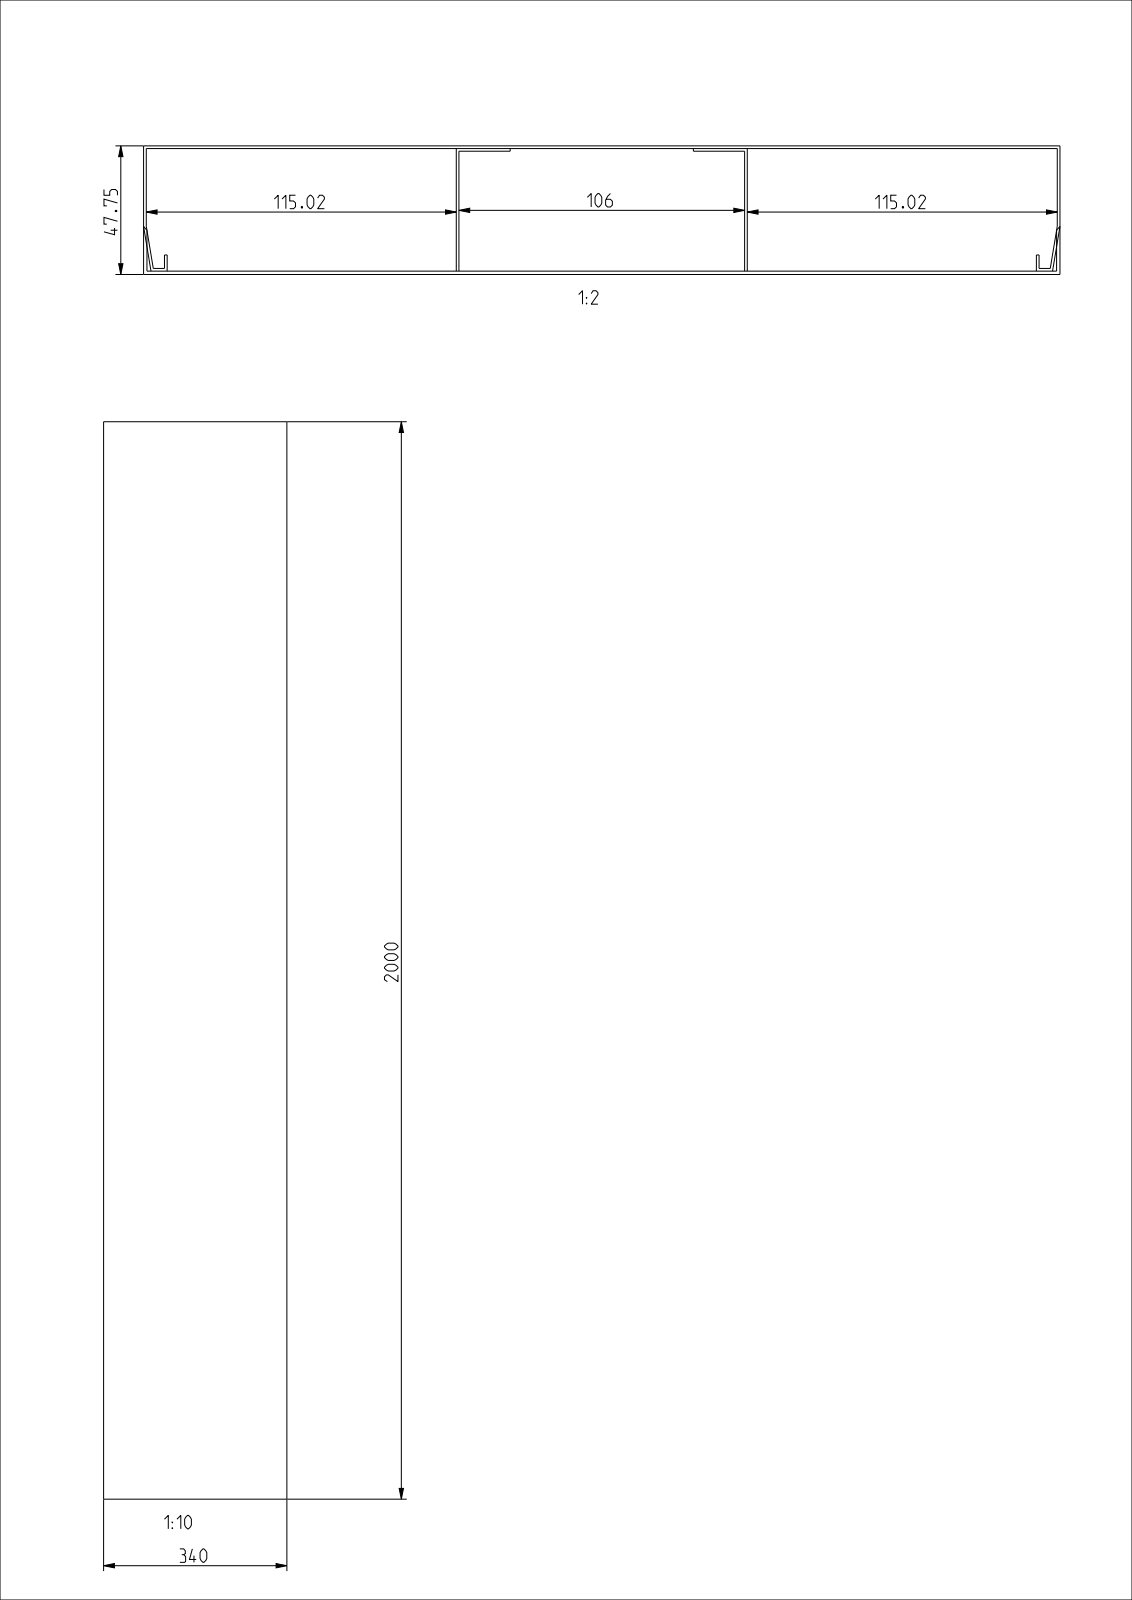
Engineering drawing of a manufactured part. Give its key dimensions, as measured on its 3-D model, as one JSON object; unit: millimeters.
{"part_name": "UK340483KUN_UNTERTEIL; UK340482KUN_OBERTEIL; UK340483KUN_ASM", "step_written_by": "CREO PARAMETRIC BY PTC INC, 2022024 (AUTOMOTIVE_DESIGN)", "units": "millimeters", "bodies": {"solids": 2, "faces": 46, "planar": 46, "cylindrical": 0, "other": 0}, "overall_size": [2000, 340, 47.75], "volume_mm3": 2086000, "surface_area_mm2": 3670000, "face_to_face_distances": [1, 1.25, 46.5, 47.75, 45.5, 46.75, 0.98, 116.02, 223.98, 117]}
